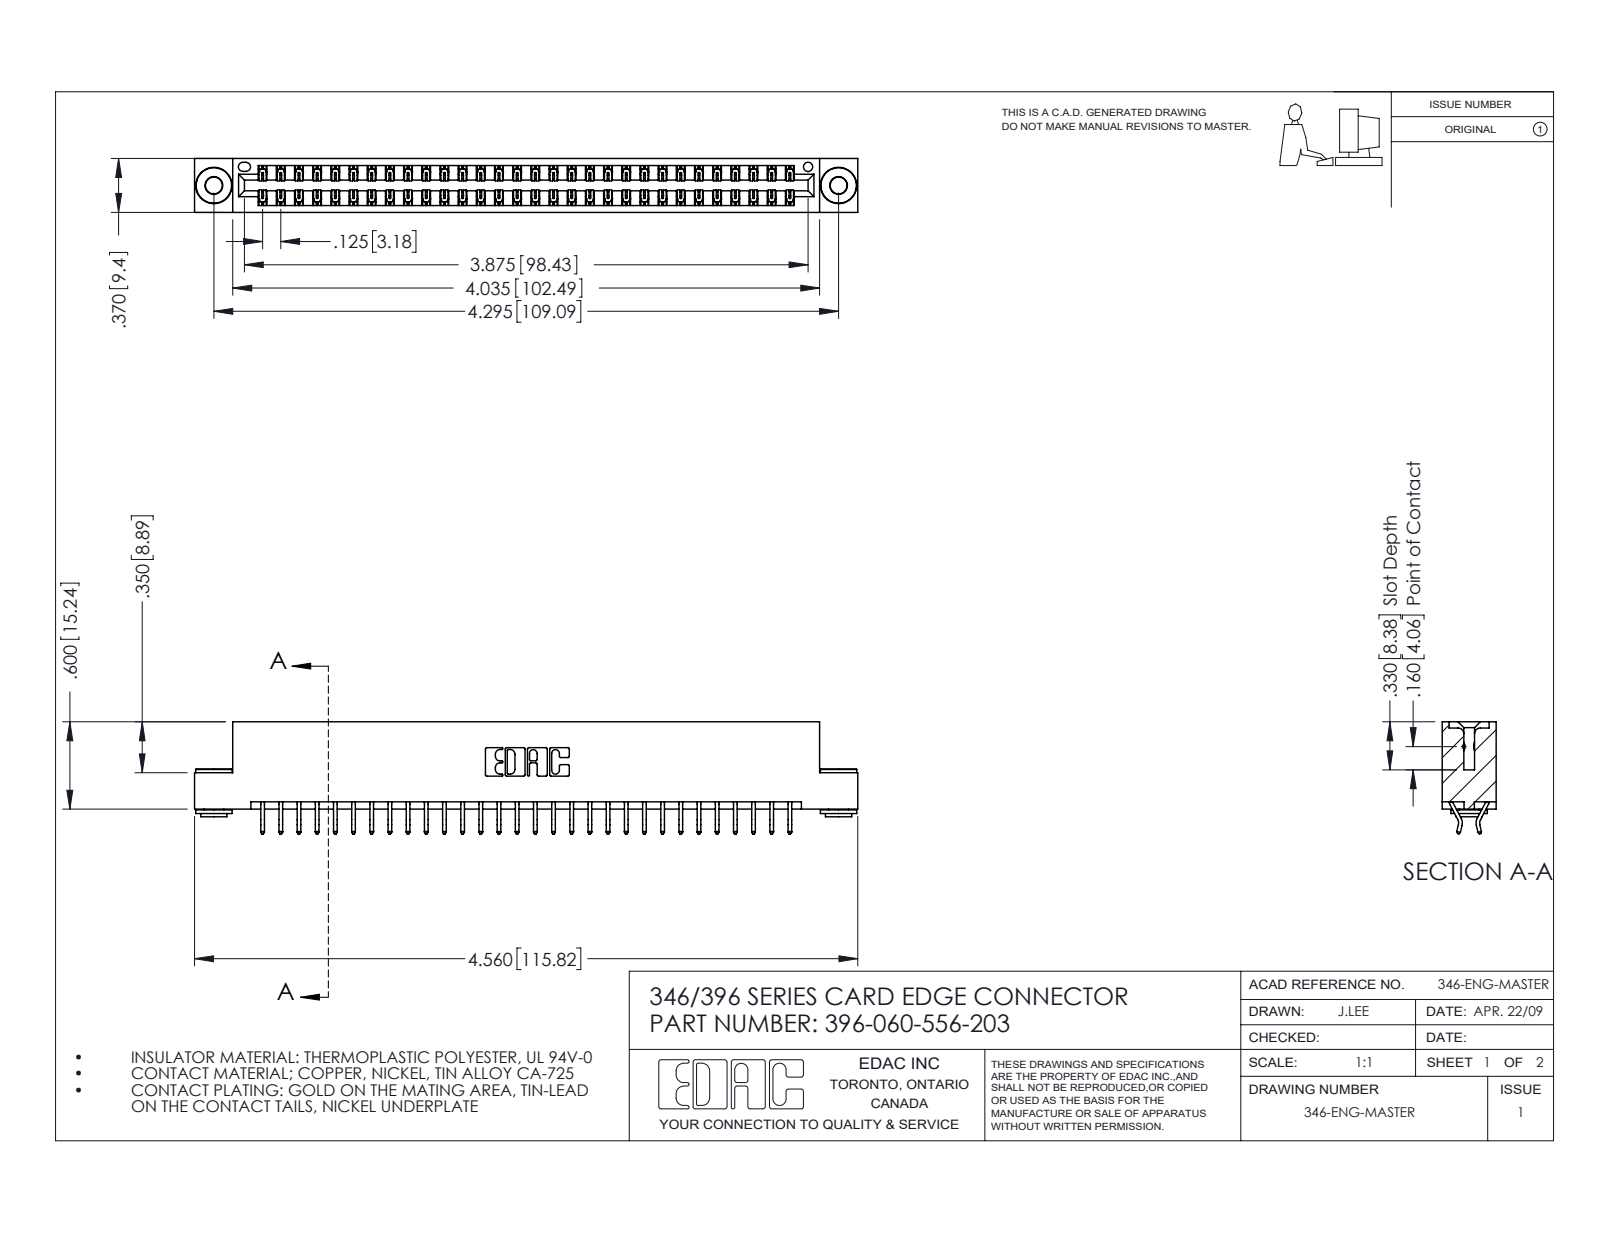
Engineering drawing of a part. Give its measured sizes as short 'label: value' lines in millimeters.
name: 345-292-001_556 Tail; 345-250-002_345-250-002-102; 396-060-556-203; 346 Part_Flush Mounting Lugs - 0.156 Dia-TH
written by: SolidWorks 2016 (CONFIG_CONTROL_DESIGN)
unit: mm
bodies: 63 solids, 3640 faces (2426 planar, 1206 cylindrical, 8 other)
size: 115.8 × 19.6 × 9.4
volume: 11 200 mm³; area: 15 390 mm²
holes: 2× ⌀2.9, 2× ⌀4, 1× ⌀1.6
bosses: 2× ⌀6.4, 2× ⌀4.6, 2× ⌀3.5
rounds: 90× R0.2, 22× R0.3, 6× R0.2, 6× R0.8, 3× R0.7, 2× R0.3, 2× R0.4, 2× R0.6
face distances: 1.2, 8.2, 9.4, 6.4, 0.6, 1.8, 7.6, 7, 3.8, 5.6
hole spacings: 6.2, 103.8, 109.1
